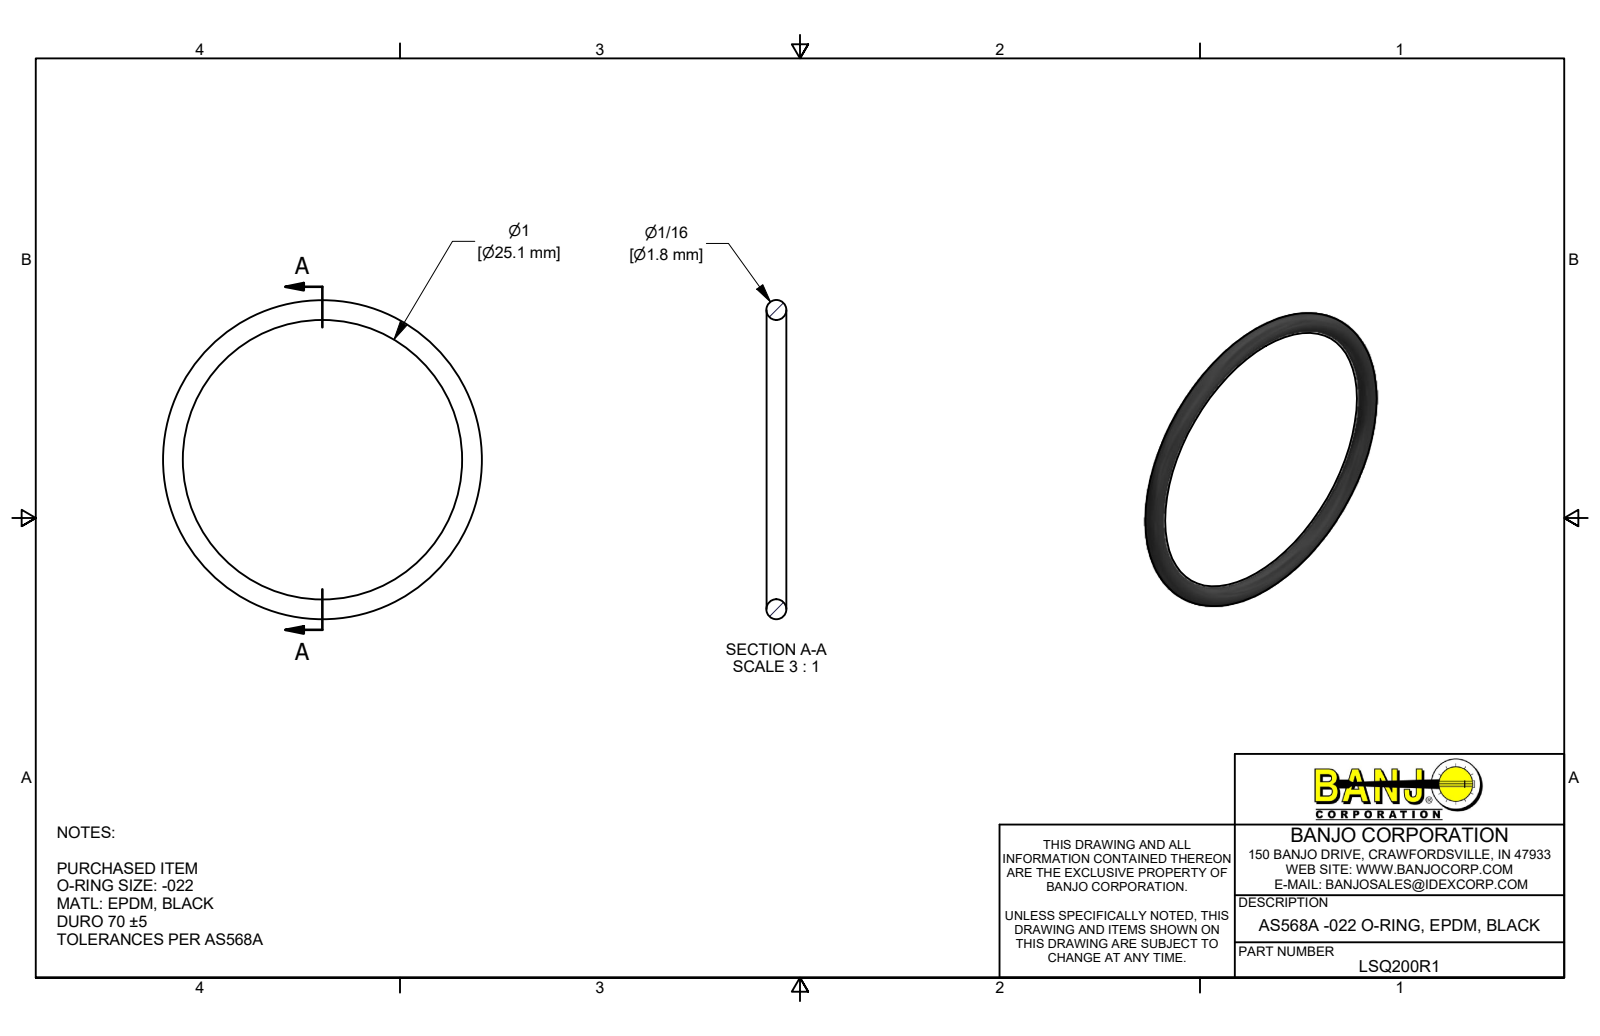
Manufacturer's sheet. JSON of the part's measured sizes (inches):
{"part_name": "LSQ200R1", "step_written_by": "Autodesk Inventor 2019 (AUTOMOTIVE_DESIGN)", "units": "inches", "bodies": {"solids": 1, "faces": 1, "planar": 0, "cylindrical": 0, "other": 1}, "overall_size": [1.129, 1.129, 0.07], "volume_in3": 0.013, "surface_area_in2": 0.732}
